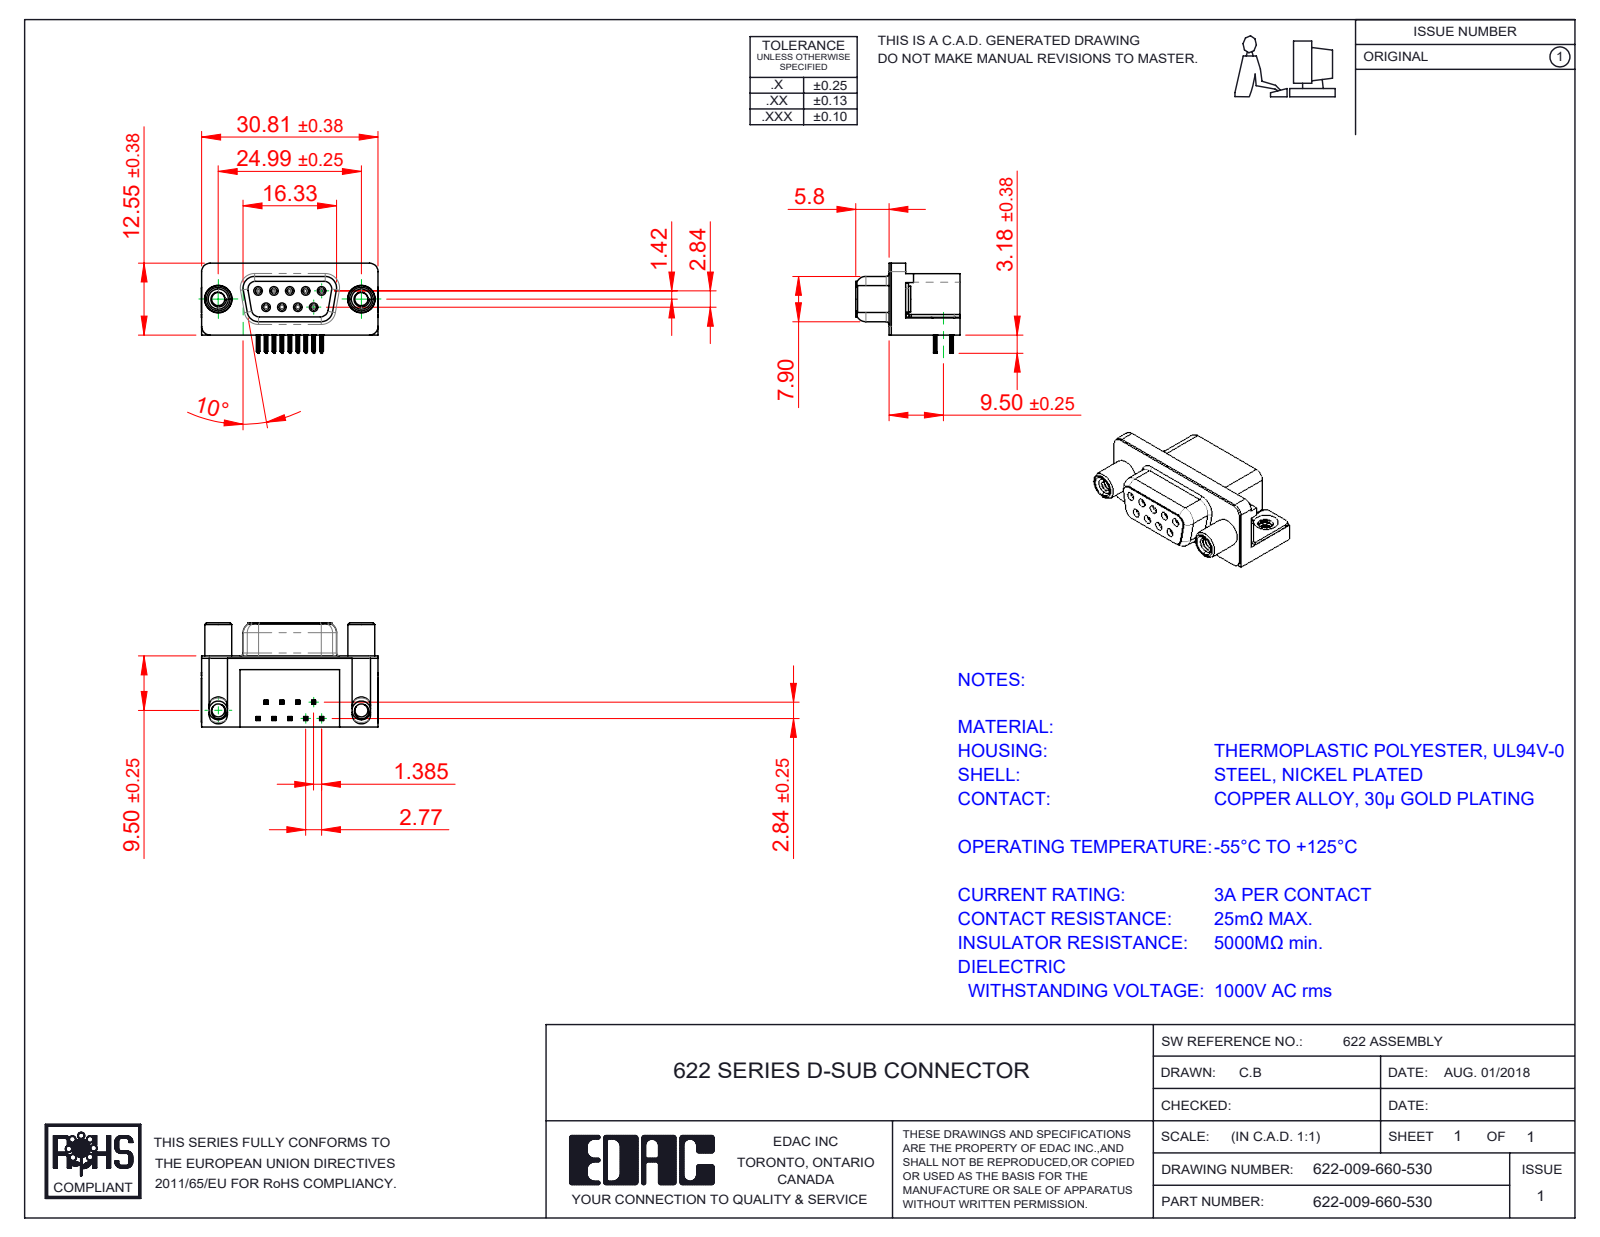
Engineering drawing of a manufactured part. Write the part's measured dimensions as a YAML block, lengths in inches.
part_name: "622 Socket Bottom; 622 Housing_9 Socket; 622 Round Threaded Standoff; 622-009-660-530 (+3 more)"
step_written_by: "SolidWorks 2016 (CONFIG_CONTROL_DESIGN)"
units: inches
bodies: {solids: 15, faces: 1606, planar: 708, cylindrical: 432, other: 466}
overall_size: [1.216, 0.717, 0.64]
volume: 0.233
surface_area: 8.181
round_holes:
  - {diameter: 0.031, count: 9}
  - {diameter: 0.035, count: 9}
  - {diameter: 0.091, count: 2}
  - {diameter: 0.122, count: 2}
  - {diameter: 0.157, count: 2}
  - {diameter: 0.189, count: 2}
  - {diameter: 0.197, count: 2}
round_bosses_or_shafts:
  - {diameter: 0.047, count: 9}
  - {diameter: 0.193, count: 2}
  - {diameter: 0.185, count: 2}
  - {diameter: 0.177, count: 2}
  - {diameter: 0.152, count: 2}
partial_cylinders:
  - {radius: 0.004, count: 72}
  - {radius: 0.006, count: 36}
  - {radius: 0.014, count: 18}
  - {radius: 0.039, count: 18}
  - {radius: 0.02, count: 10}
  - {radius: 0.013, count: 9}
  - {radius: 0.053, count: 8}
  - {radius: 0.063, count: 8}
face_to_face_distances: [0.016, 0.472, 0.488, 0.014, 0.114, 0.098, 0.407, 0.374, 0.244, 0.228]
hole_center_spacings: [0.124, 0.109, 0.218, 0.198, 0.198, 0.327, 0.294, 0.295]
